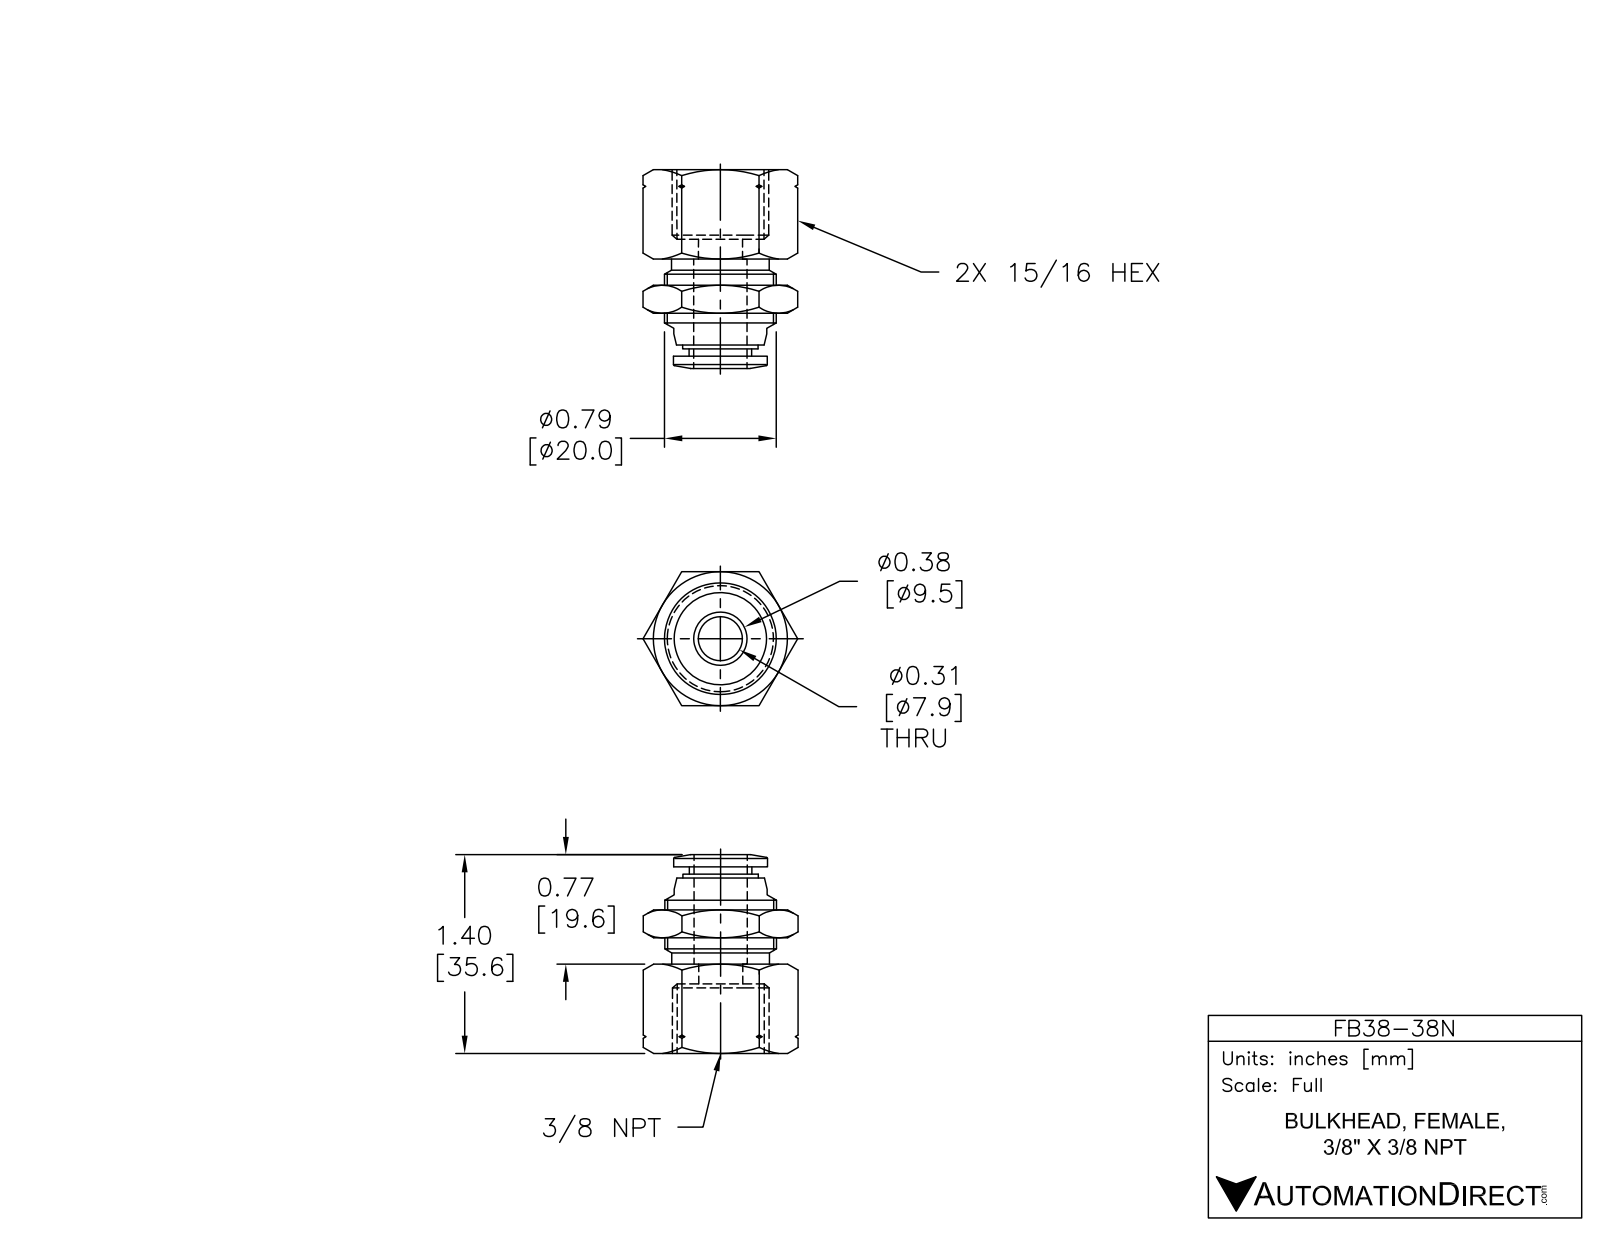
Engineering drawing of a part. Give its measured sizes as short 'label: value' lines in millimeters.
name: FB38-38N
written by: SolidWorks 2015 (AUTOMOTIVE_DESIGN)
unit: mm
bodies: 1 solid, 91 faces (21 planar, 18 cylindrical, 52 other)
size: 35.6 × 27.7 × 24
volume: 9 370 mm³; area: 5 343 mm²
holes: 1× ⌀8, 1× ⌀9.8
bosses: 1× ⌀20, 1× ⌀16.8, 1× ⌀16.7, 1× ⌀16.4, 1× ⌀13.5, 1× ⌀11.2
face distances: 24, 16, 12.5, 3.5, 20.5, 8, 4.5, 25.5, 13, 9.5
